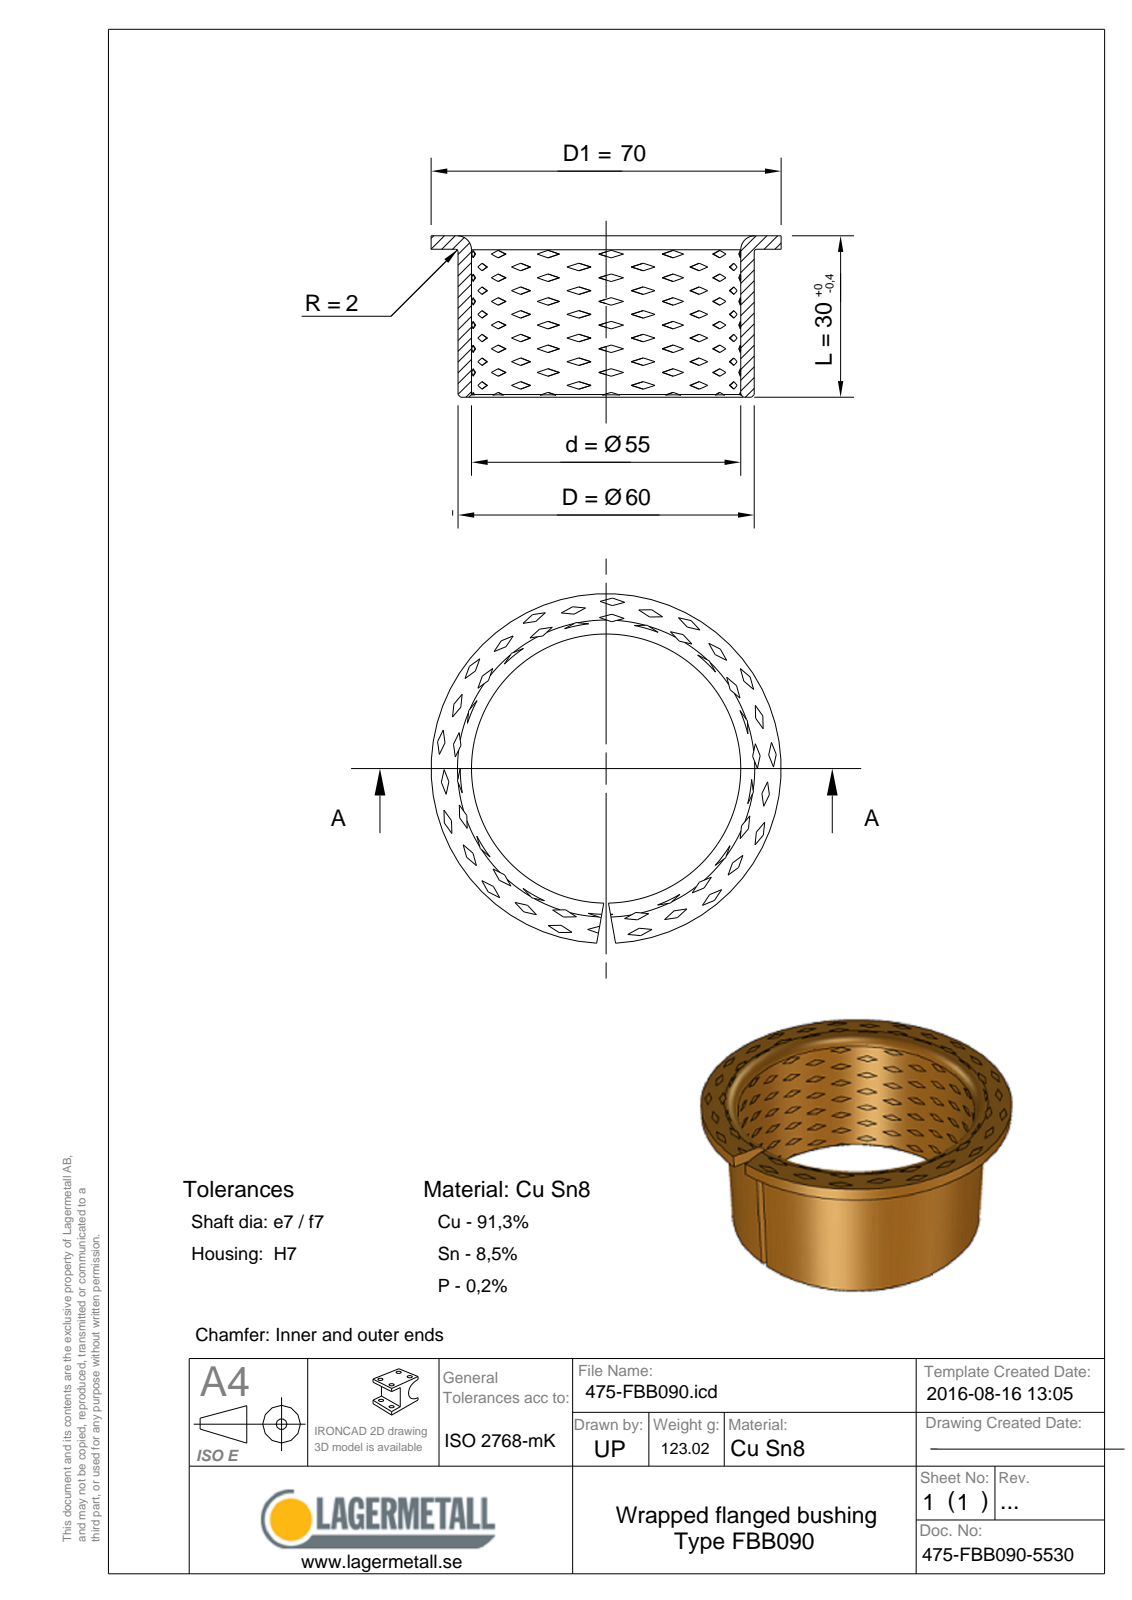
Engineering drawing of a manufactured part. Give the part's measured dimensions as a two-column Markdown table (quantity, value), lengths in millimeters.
| quantity | value |
| --- | --- |
| part name | 475-FBB090-5530 |
| STEP written by | Spatial InterOp 3D (CONFIG_CONTROL_DESIGN) |
| units | millimeters |
| bodies | 1 solid, 12 faces (5 planar, 3 cylindrical, 4 other) |
| overall size | 70 × 69.96 × 30 |
| volume | 15 187 mm³ |
| surface area | 13 247 mm² |
| round holes (diameter × count) | 55 × 1 |
| round bosses / shafts (diameter × count) | 70 × 1, 60 × 1 |
| main face-to-face distances | 2.5, 27.5, 30 |
